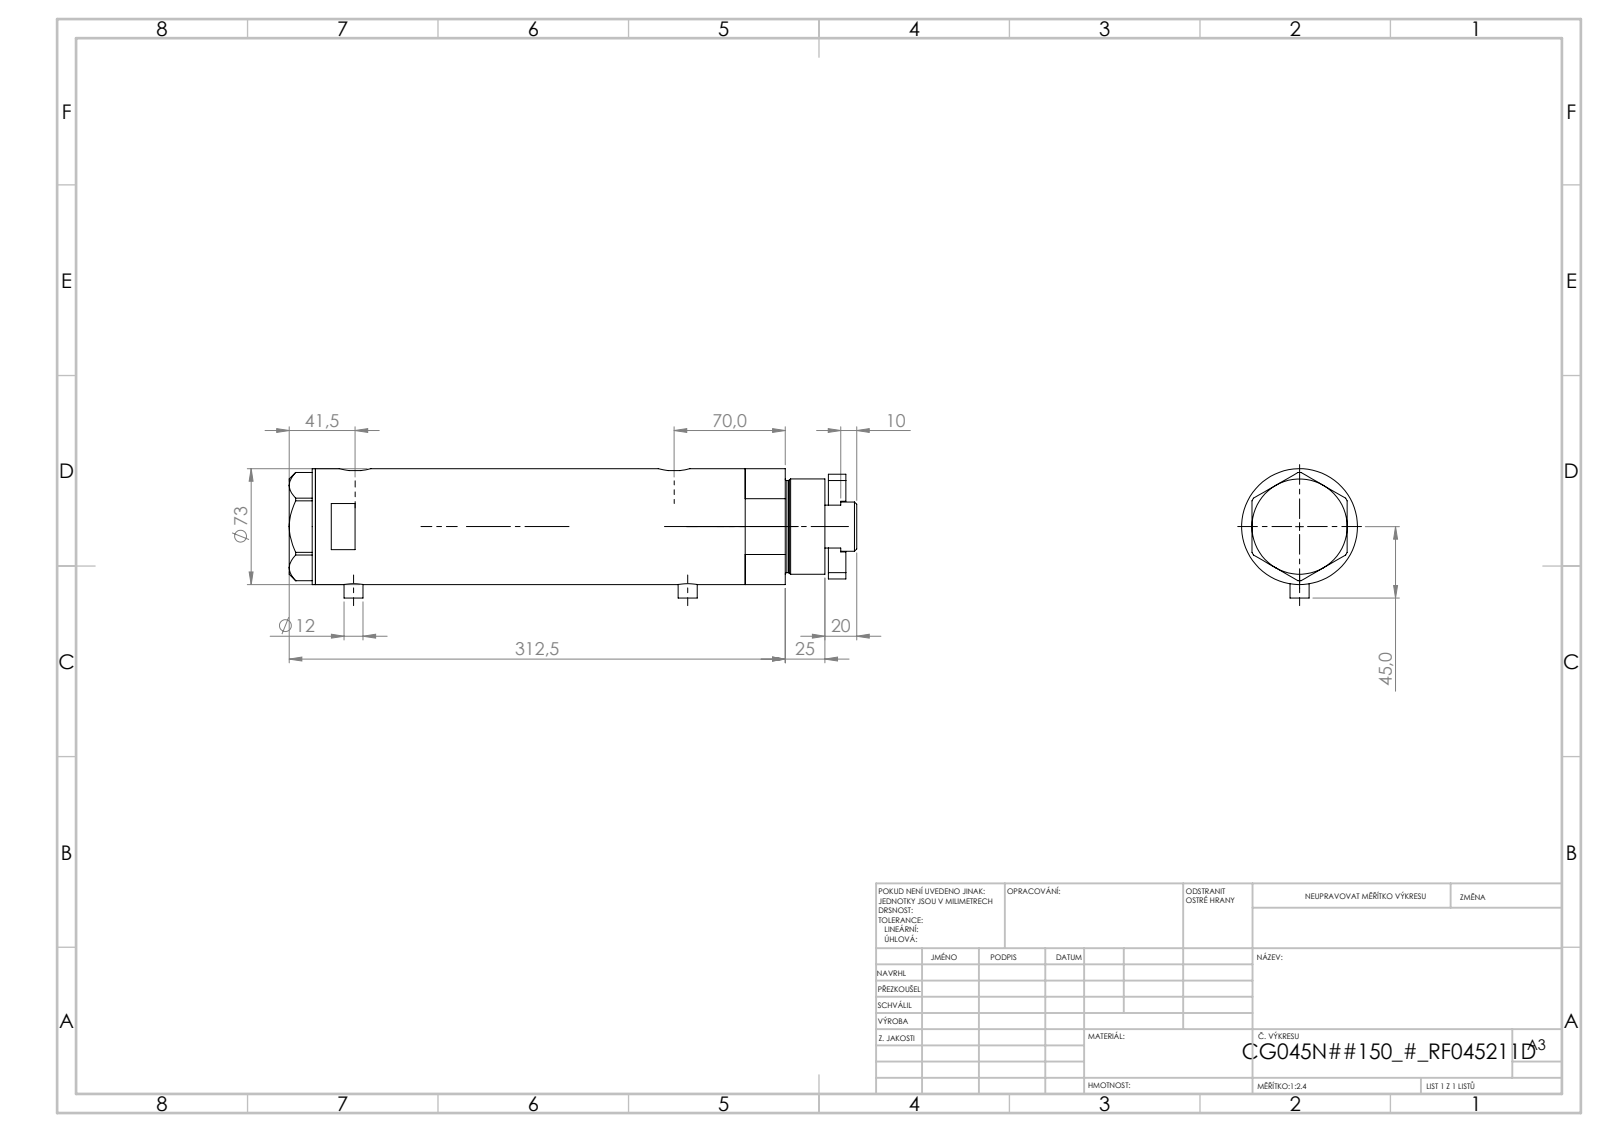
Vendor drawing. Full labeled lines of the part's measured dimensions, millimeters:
Part name (STEP PRODUCT): V270CG_VC; V270CG_BACK; V270CG_FRONT; V270CG_MIDDLE (+1 more)
STEP written by: SolidWorks 2019 (CONFIG_CONTROL_DESIGN)
Units: millimetres
Bodies: 6 solids, 160 faces (73 planar, 67 cylindrical, 20 other)
Overall size (bounding box): 357.5 × 81.5 × 73
Volume: 1 254 000 mm³ · Surface area: 204 482 mm²
Round holes (diameter × count): ⌀8.1 ×4, ⌀13.5 ×4, ⌀12.5 ×2, ⌀13.16 ×2, ⌀10.5 ×1, ⌀32 ×1, ⌀33.5 ×1, ⌀45 ×1, ⌀48 ×1, ⌀64 ×1
Round bosses / shafts (diameter × count): ⌀12 ×2, ⌀73 ×1, ⌀60 ×1, ⌀58 ×1, ⌀31 ×1
Partial cylindrical surfaces — rounded edges, fillets, slot ends (radius × count): R10 ×2
Main face-to-face distances: 226, 26, 200, 16.5, 42.5, 242.5, 321, 2, 337.5, 295
Hole centre spacings: 25.14, 15, 47.98, 50.27, 1, 8.5, 201, 202
